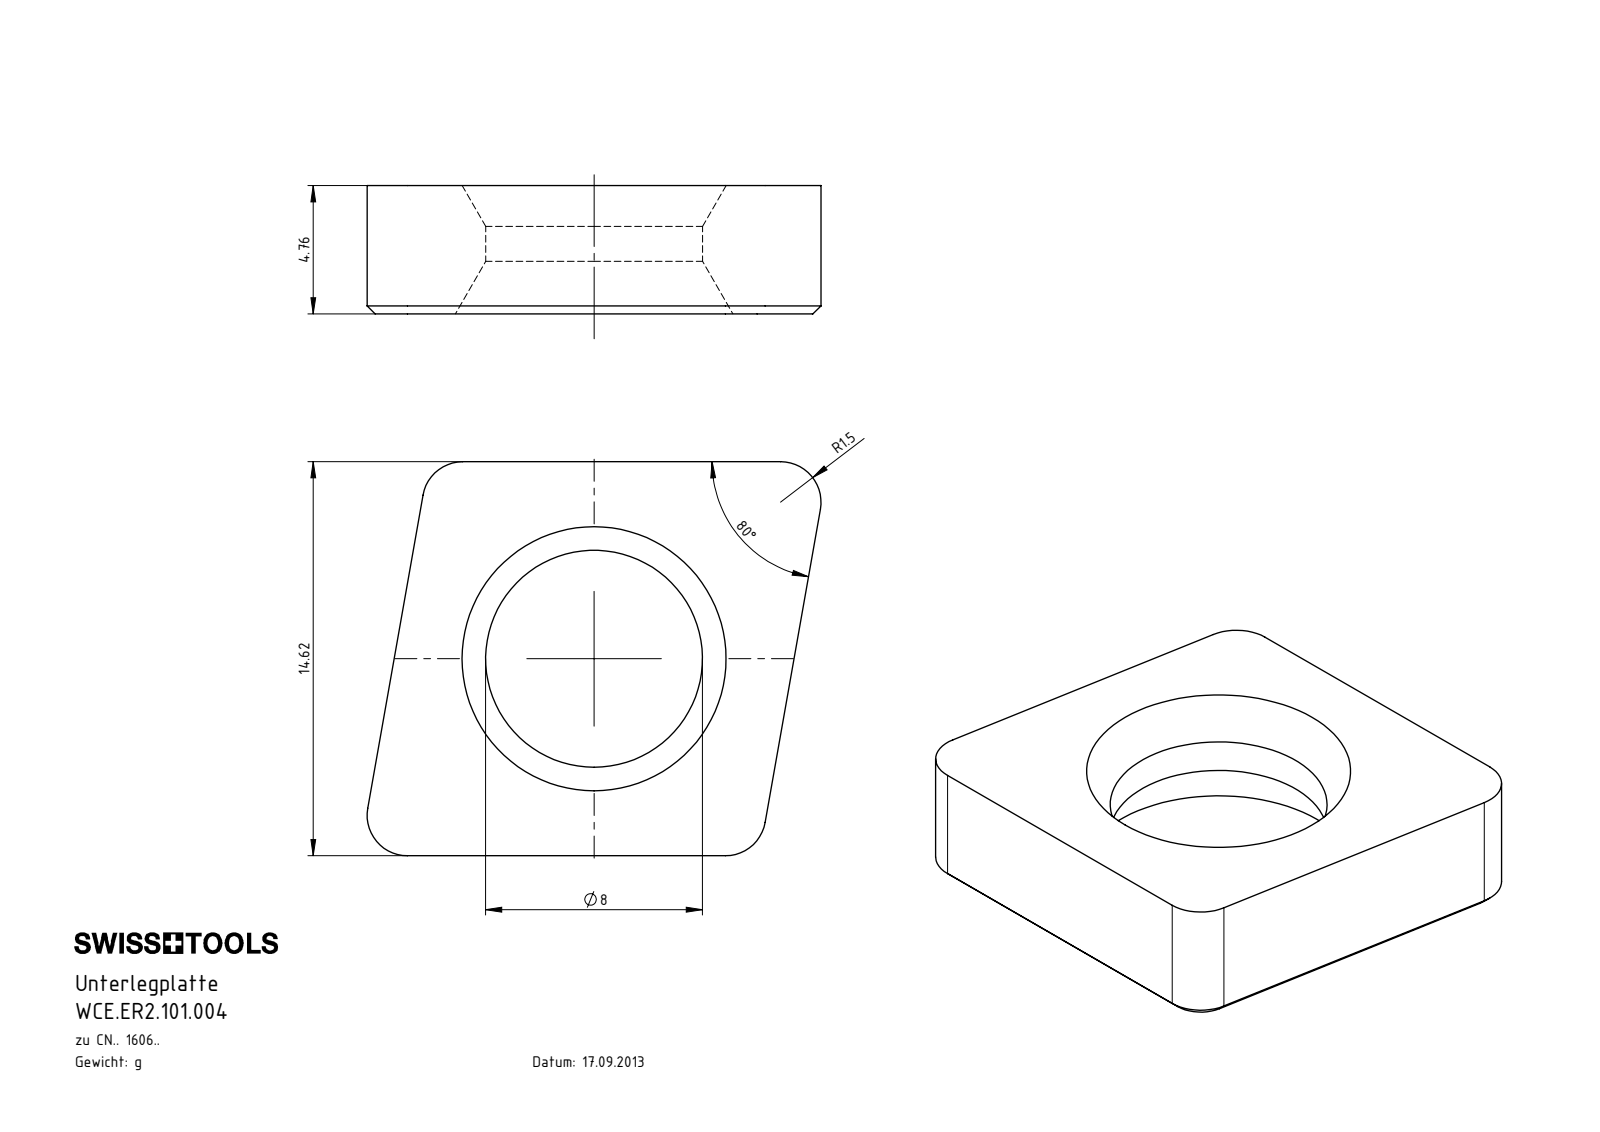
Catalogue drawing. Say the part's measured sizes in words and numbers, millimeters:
The part is named "WCE.ER2.101.004". Its 3-D file was written by "SolidWorks 2017 (AUTOMOTIVE_DESIGN)". It is 1 solid with 21 faces: 10 planar, 5 cylindrical and 6 other. Overall it measures 16.85 by 14.62 by 4.76 millimeters. Its volume is 730 cubic millimeters and its surface area 677 square millimeters. Round holes: 1 of diameter 8.05. Partial cylindrical surfaces (rounded edges, fillets, slot ends): 4 of radius 1.5. The main face-to-face distances are 4.76, 14.62.
